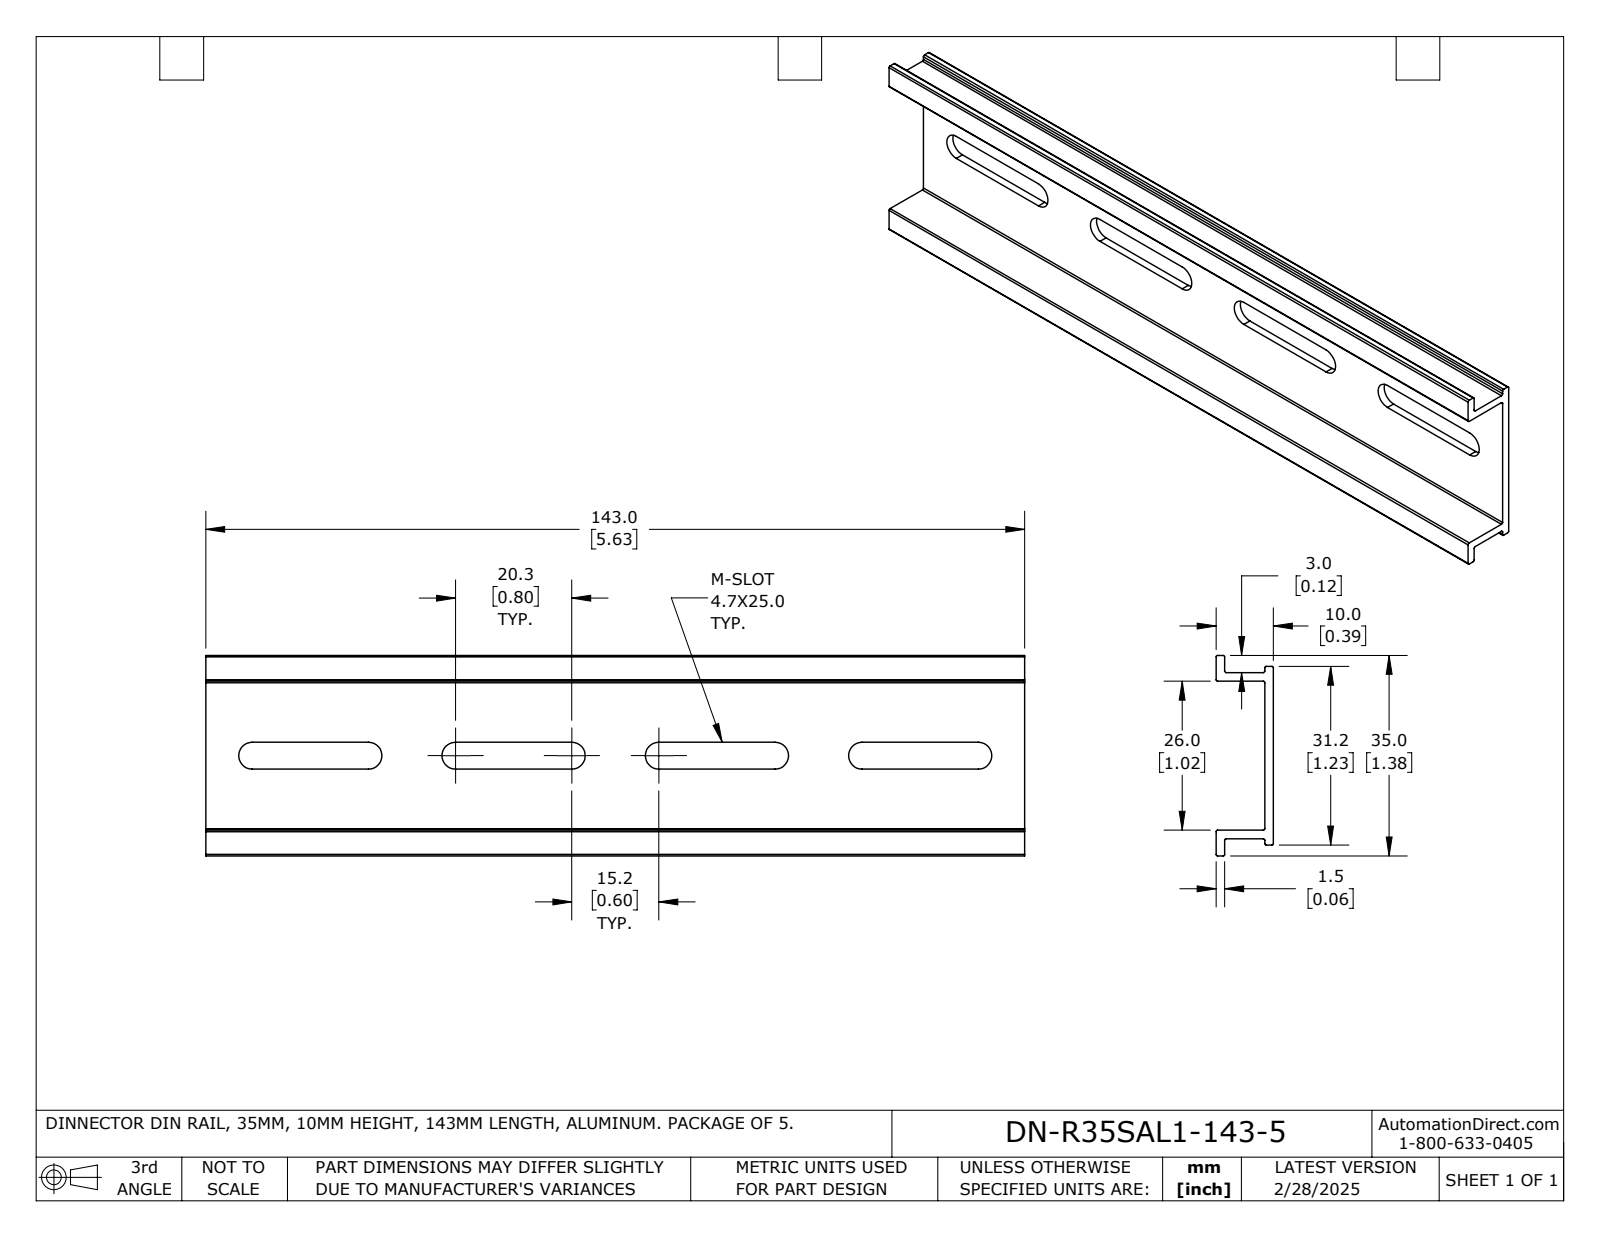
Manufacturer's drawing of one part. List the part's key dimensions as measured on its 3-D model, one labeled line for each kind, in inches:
Part name (STEP PRODUCT): DN-R35SAL1-143-5_Default
STEP written by: SolidWorks 2024 (CONFIG_CONTROL_DESIGN)
Units: inches
Bodies: 1 solid, 50 faces (26 planar, 24 cylindrical, 0 other)
Overall size (bounding box): 5.63 × 1.378 × 0.394
Volume: 0.668 in³ · Surface area: 23.65 in²
Partial cylindrical surfaces — rounded edges, fillets, slot ends (radius × count): R0.011 ×16, R0.093 ×8
Main face-to-face distances: 0.059, 1.083, 0.335, 1.024, 0.394, 1.142, 0.276, 0.043, 0.102, 1.126
